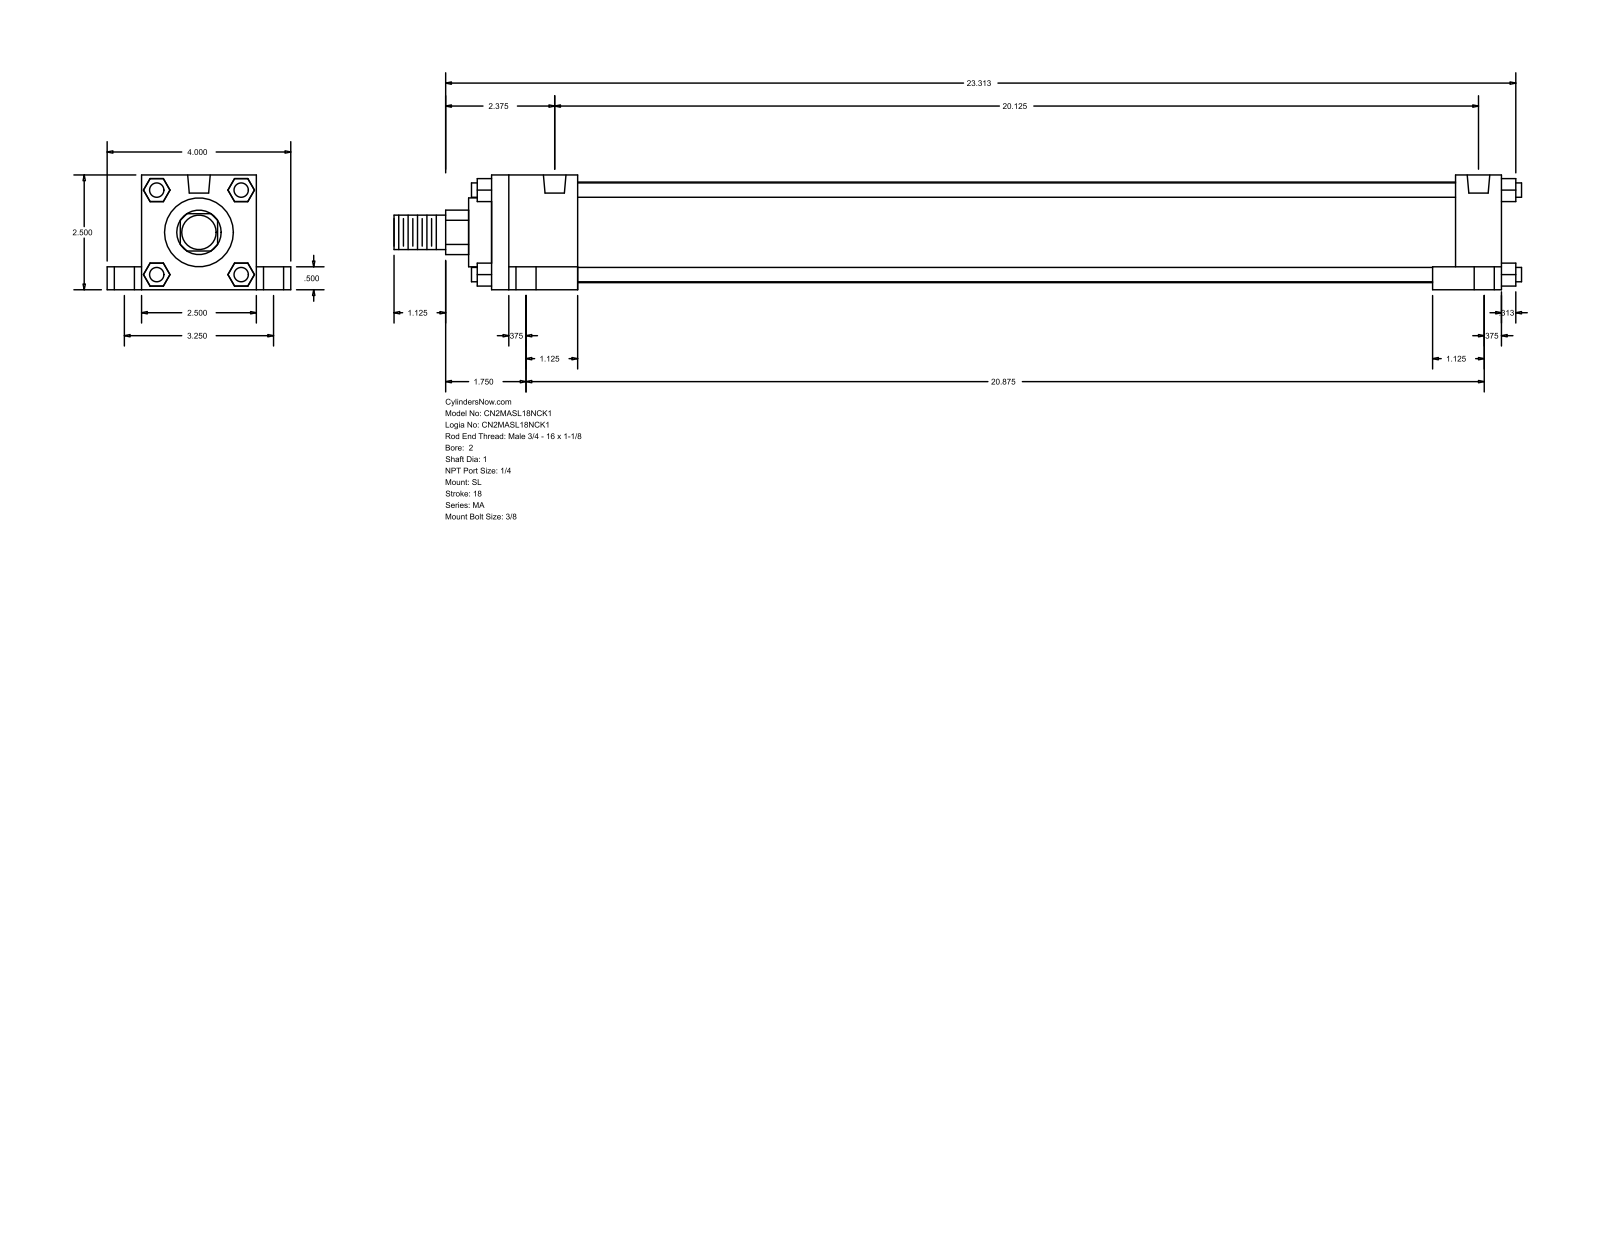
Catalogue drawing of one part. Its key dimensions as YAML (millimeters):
part_name: "MA_SL__0200_1"
step_written_by: "GSSL Pune (CONFIG_CONTROL_DESIGN)"
units: millimeters
bodies: {solids: 0, faces: 148, planar: 112, cylindrical: 36, other: 0}
overall_size: [623.89, 101.6, 63.5]
round_holes:
  - {diameter: 7.94, count: 4}
  - {diameter: 11.11, count: 4}
  - {diameter: 17.46, count: 4}
  - {diameter: 12.49, count: 2}
round_bosses_or_shafts:
  - {diameter: 7.94, count: 4}
  - {diameter: 55.63, count: 1}
  - {diameter: 38.1, count: 1}
  - {diameter: 25.4, count: 1}
  - {diameter: 19.05, count: 1}
partial_cylinders:
  - {radius: 12.29, count: 1}
face_to_face_distances: [63.5, 12.7, 558.8, 19.05, 82.55, 25.4, 50.8, 47.63, 511.17, 533.4]
hole_center_spacings: [41.39, 44.22, 82.54, 511.17, 515.99, 528.66, 530.22, 536.61]
